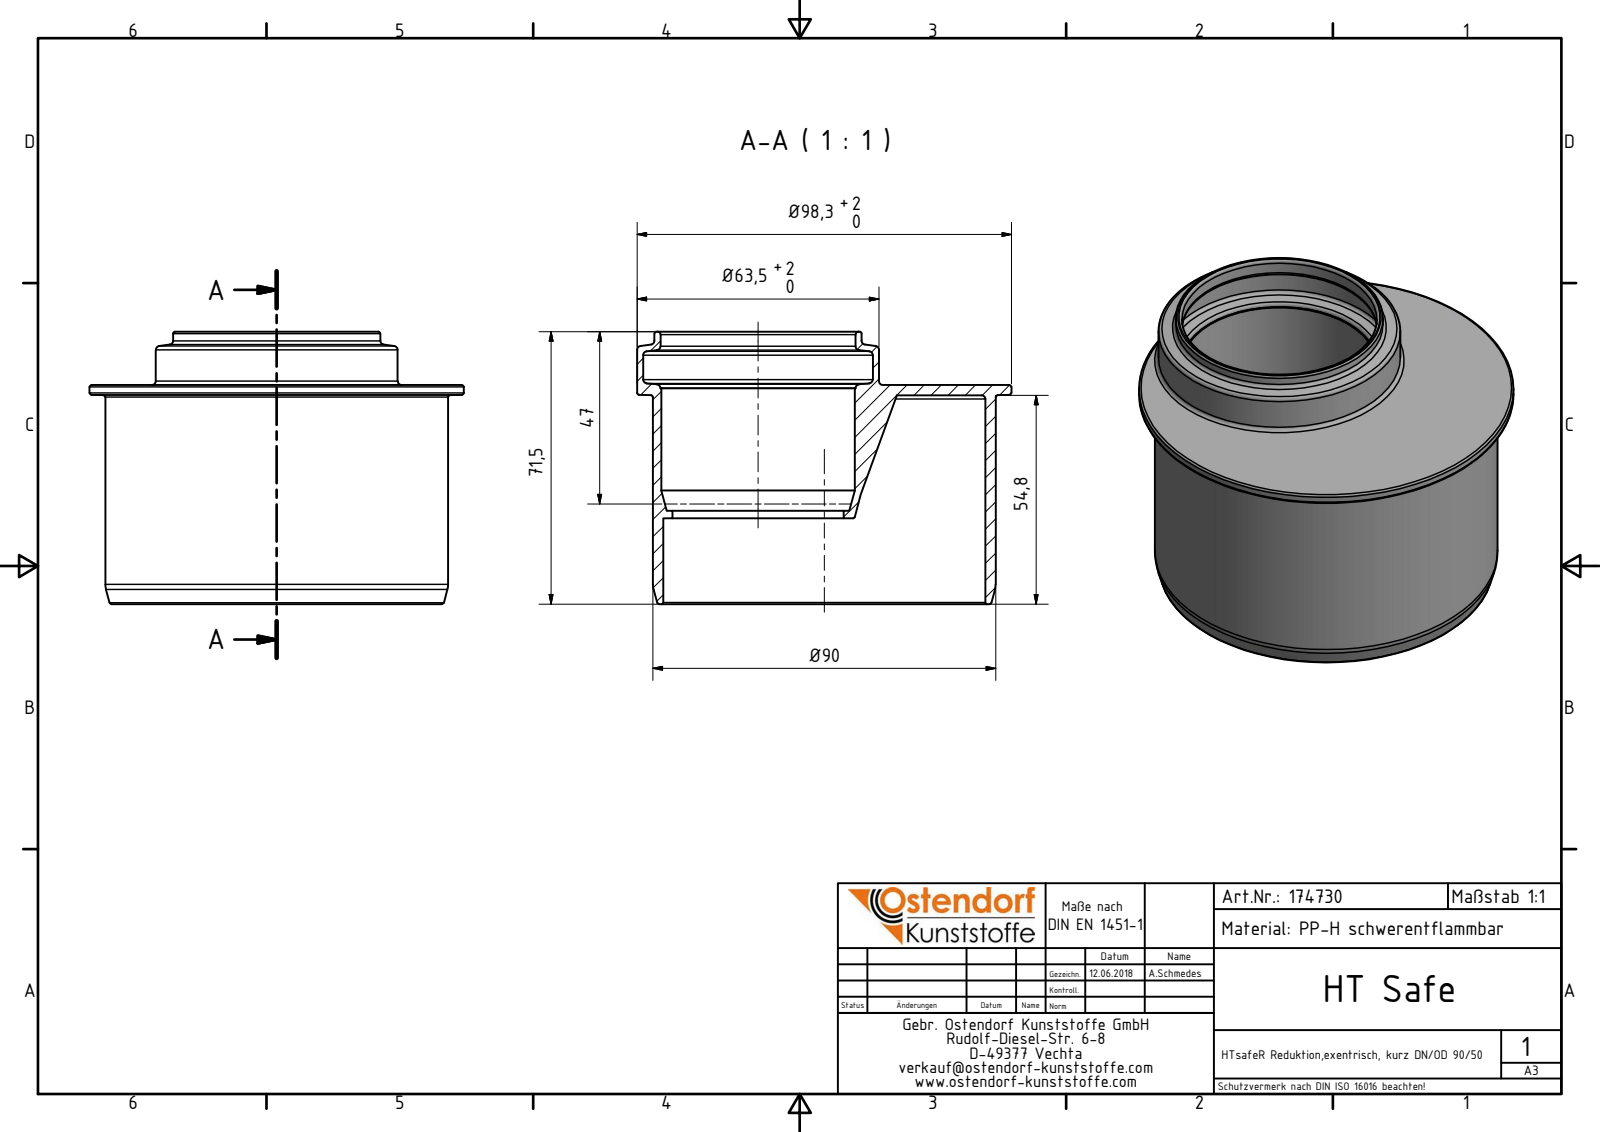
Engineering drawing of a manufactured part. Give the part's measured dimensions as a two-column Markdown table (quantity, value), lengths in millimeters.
| quantity | value |
| --- | --- |
| part name | 174730 HTsafeR-Reduktion, exentrisch, kurz DN_OD 90_50 |
| STEP written by | Autodesk Inventor 2016 (AUTOMOTIVE_DESIGN) |
| units | millimeters |
| bodies | 1 solid, 93 faces (32 planar, 18 cylindrical, 43 other) |
| overall size | 98.3 × 98.3 × 71.5 |
| volume | 69 033 mm³ |
| surface area | 57 325 mm² |
| round holes (diameter × count) | 45 × 1, 50.8 × 1, 51.2 × 1, 60.3 × 1, 84.6 × 1 |
| round bosses / shafts (diameter × count) | 98.3 × 1, 90 × 1, 63.5 × 1, 54.4 × 1 |
| partial cylindrical surfaces (radius × count) | 1 × 2, 27 × 1 |
| main face-to-face distances | 2.7, 1.2, 32.3, 35, 2, 30.3, 33, 22.5, 24.5, 54.8 |
| hole center spacings | 17.4 |
